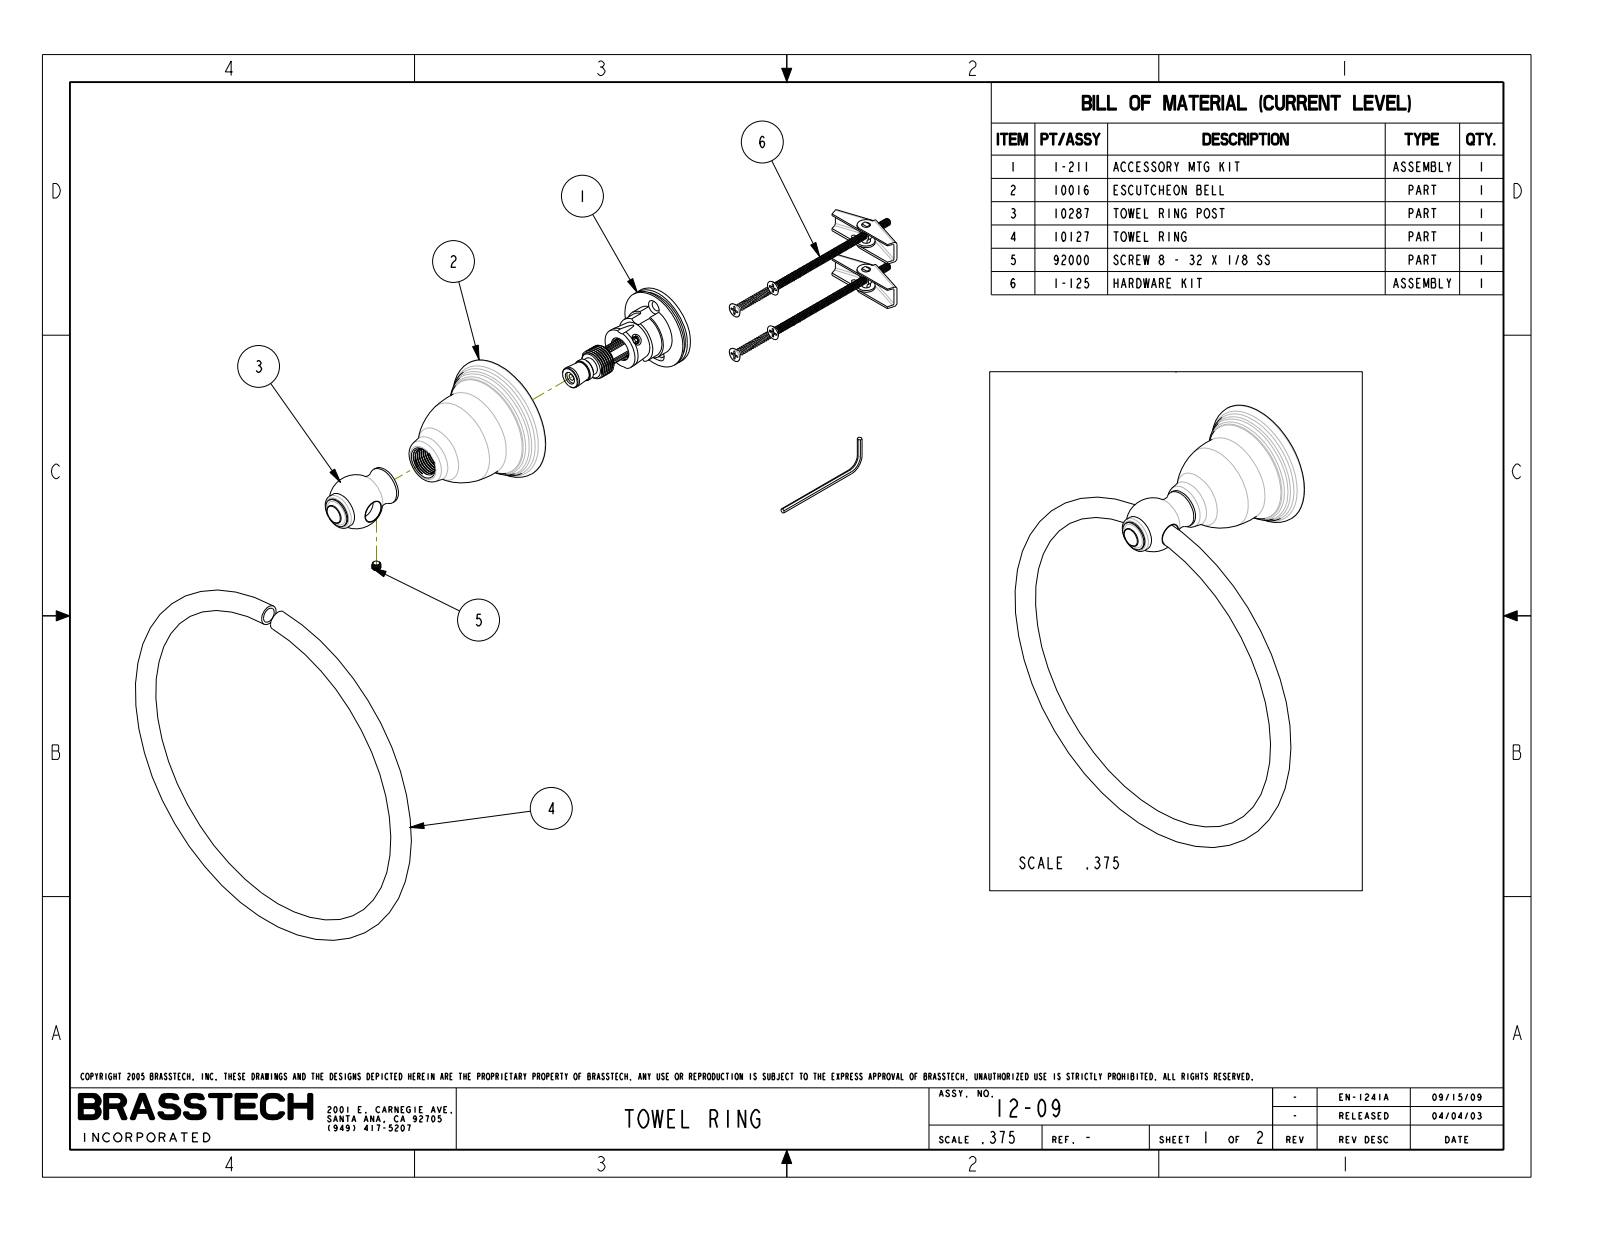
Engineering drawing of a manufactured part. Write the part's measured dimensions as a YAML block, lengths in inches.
part_name: "12-09_WEB"
step_written_by: "PRO/ENGINEER BY PARAMETRIC TECHNOLOGY CORPORATION, 2009300 (CONFIG_CONTROL_DESIGN)"
units: inches
bodies: {solids: 0, faces: 60, planar: 8, cylindrical: 8, other: 44}
overall_size: [7.98, 7, 3.333]
round_bosses_or_shafts:
  - {diameter: 2.34, count: 1}
  - {diameter: 0.705, count: 1}
  - {diameter: 0.661, count: 1}
  - {diameter: 0.545, count: 1}
face_to_face_distances: [3.243, 3.267, 0.024, 0.894, 3.333, 0.09, 0.066]
